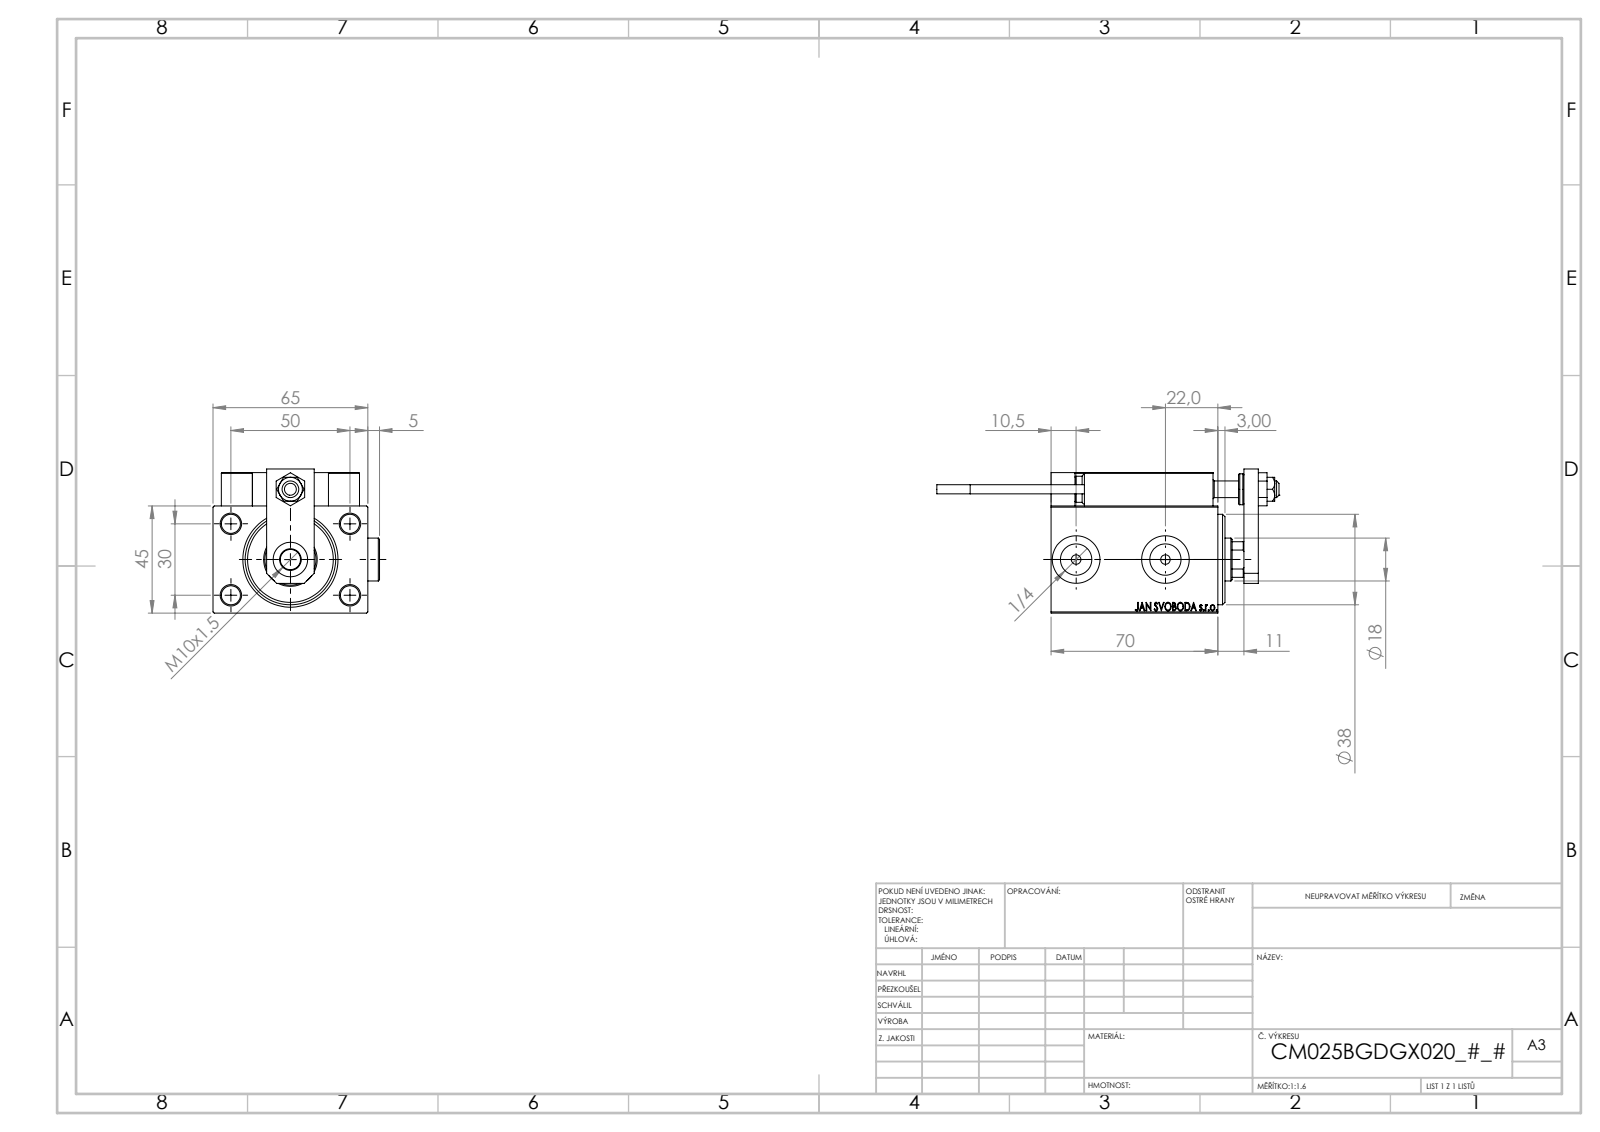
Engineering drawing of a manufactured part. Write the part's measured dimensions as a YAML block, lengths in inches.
part_name: "SWITCH X; V450CM_B_VCP; TYC_L79; SWITCH_X_FRONT_BACK (+8 more)"
step_written_by: "SolidWorks 2019 (CONFIG_CONTROL_DESIGN)"
units: inches
bodies: {solids: 26, faces: 1372, planar: 595, cylindrical: 200, other: 577}
overall_size: [5.657, 2.752, 2.382]
volume: 14.49
surface_area: 104.2
round_holes:
  - {diameter: 0.315, count: 9}
  - {diameter: 0.157, count: 6}
  - {diameter: 0.126, count: 4}
  - {diameter: 0.197, count: 2}
  - {diameter: 0.518, count: 2}
  - {diameter: 0.787, count: 2}
  - {diameter: 0.276, count: 1}
  - {diameter: 0.335, count: 1}
  - {diameter: 0.571, count: 1}
  - {diameter: 0.709, count: 1}
  - {diameter: 0.846, count: 1}
  - {diameter: 0.886, count: 1}
round_bosses_or_shafts:
  - {diameter: 0.709, count: 2}
  - {diameter: 0.197, count: 2}
  - {diameter: 0.15, count: 2}
  - {diameter: 0.512, count: 1}
  - {diameter: 0.433, count: 1}
partial_cylinders:
  - {radius: 0.012, count: 30}
  - {radius: 0.118, count: 2}
  - {radius: 0.335, count: 1}
face_to_face_distances: [1.772, 2.323, 0.551, 2.559, 0.236, 0.197, 0.748, 0.512, 0.138, 2.283]
hole_center_spacings: [1.148, 0.448, 0.787, 0.87, 1.138, 1.165, 1.169, 1.181]
